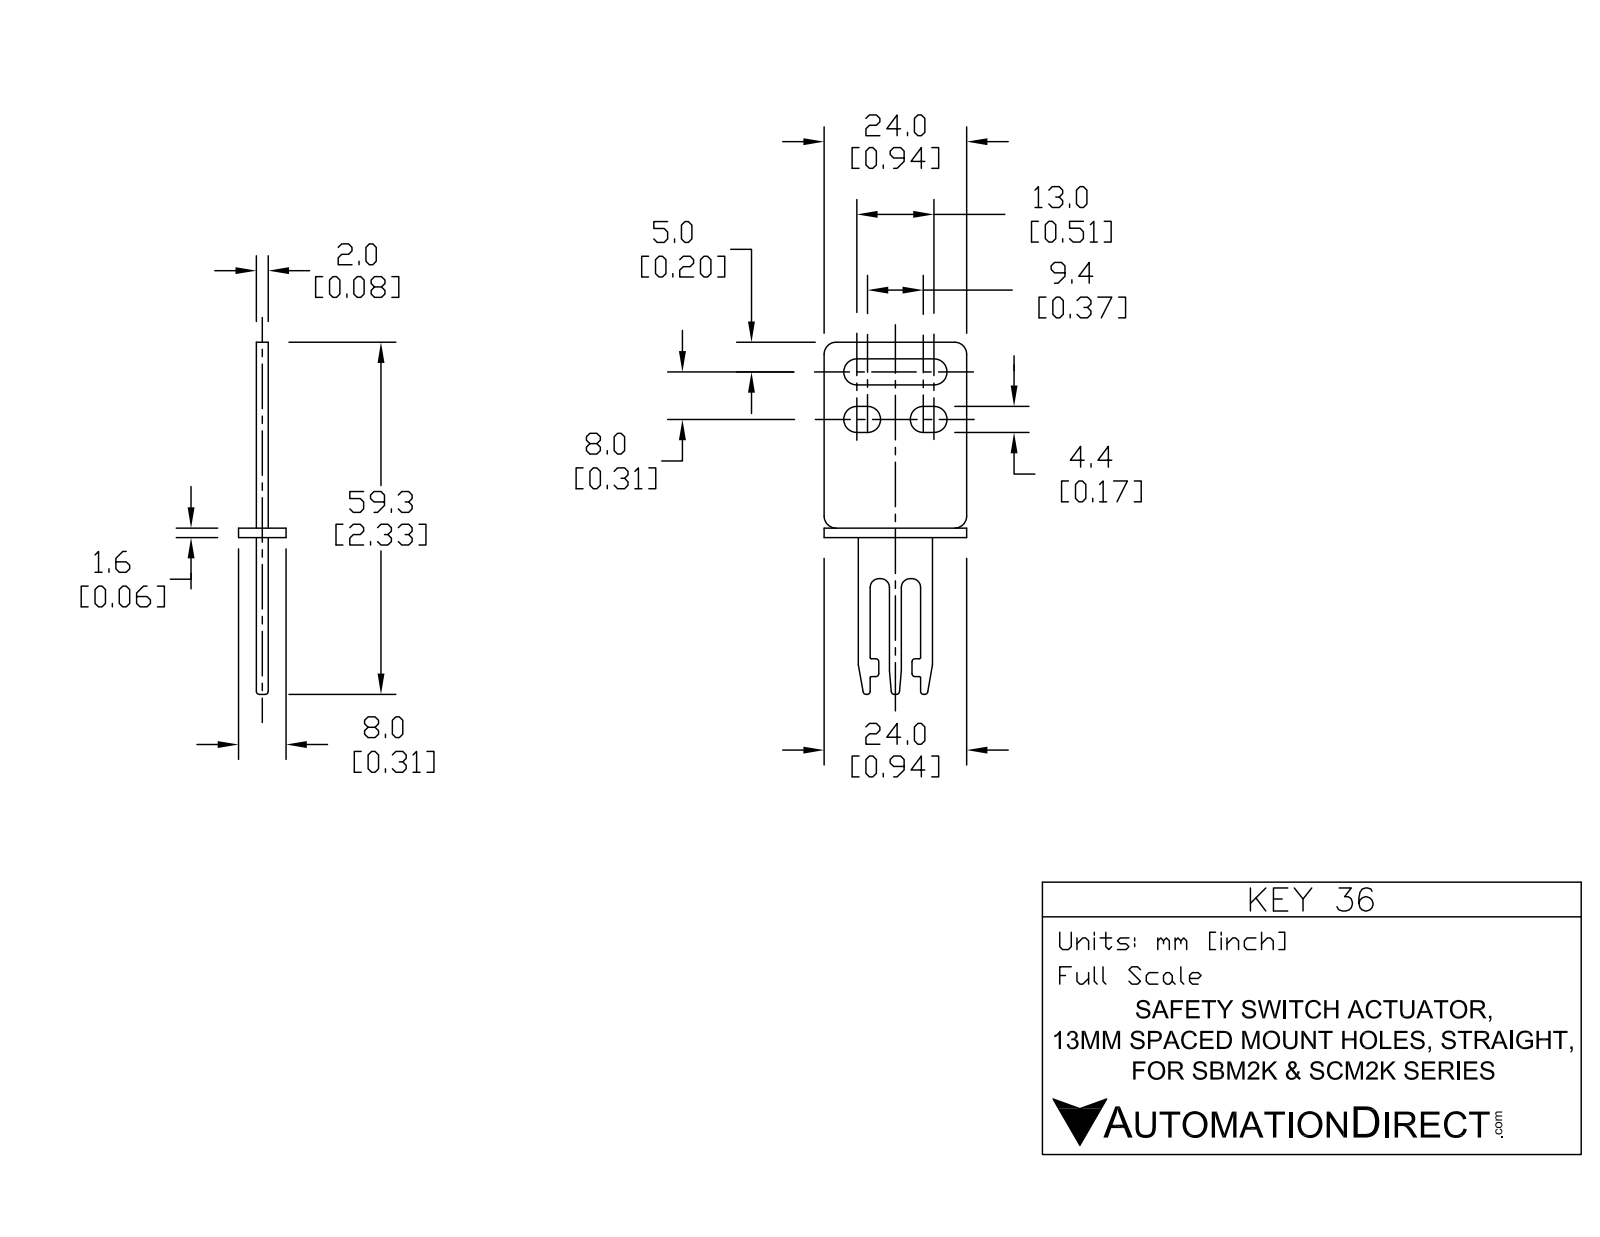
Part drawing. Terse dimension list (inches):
name: KEY36
written by: SolidWorks 2019 (CONFIG_CONTROL_DESIGN)
unit: in
bodies: 2 solids, 171 faces (58 planar, 79 cylindrical, 34 other)
size: 2.335 × 0.945 × 0.315
volume: 0.12 in³; area: 4.32 in²
rounds: 42× R0.02, 8× R0.039, 6× R0.087, 4× R0.008, 4× R0.059
face distances: 0.079, 0.063, 0.118, 0.197, 0.945, 0.226, 0.719, 0.207, 0.315, 0.083
